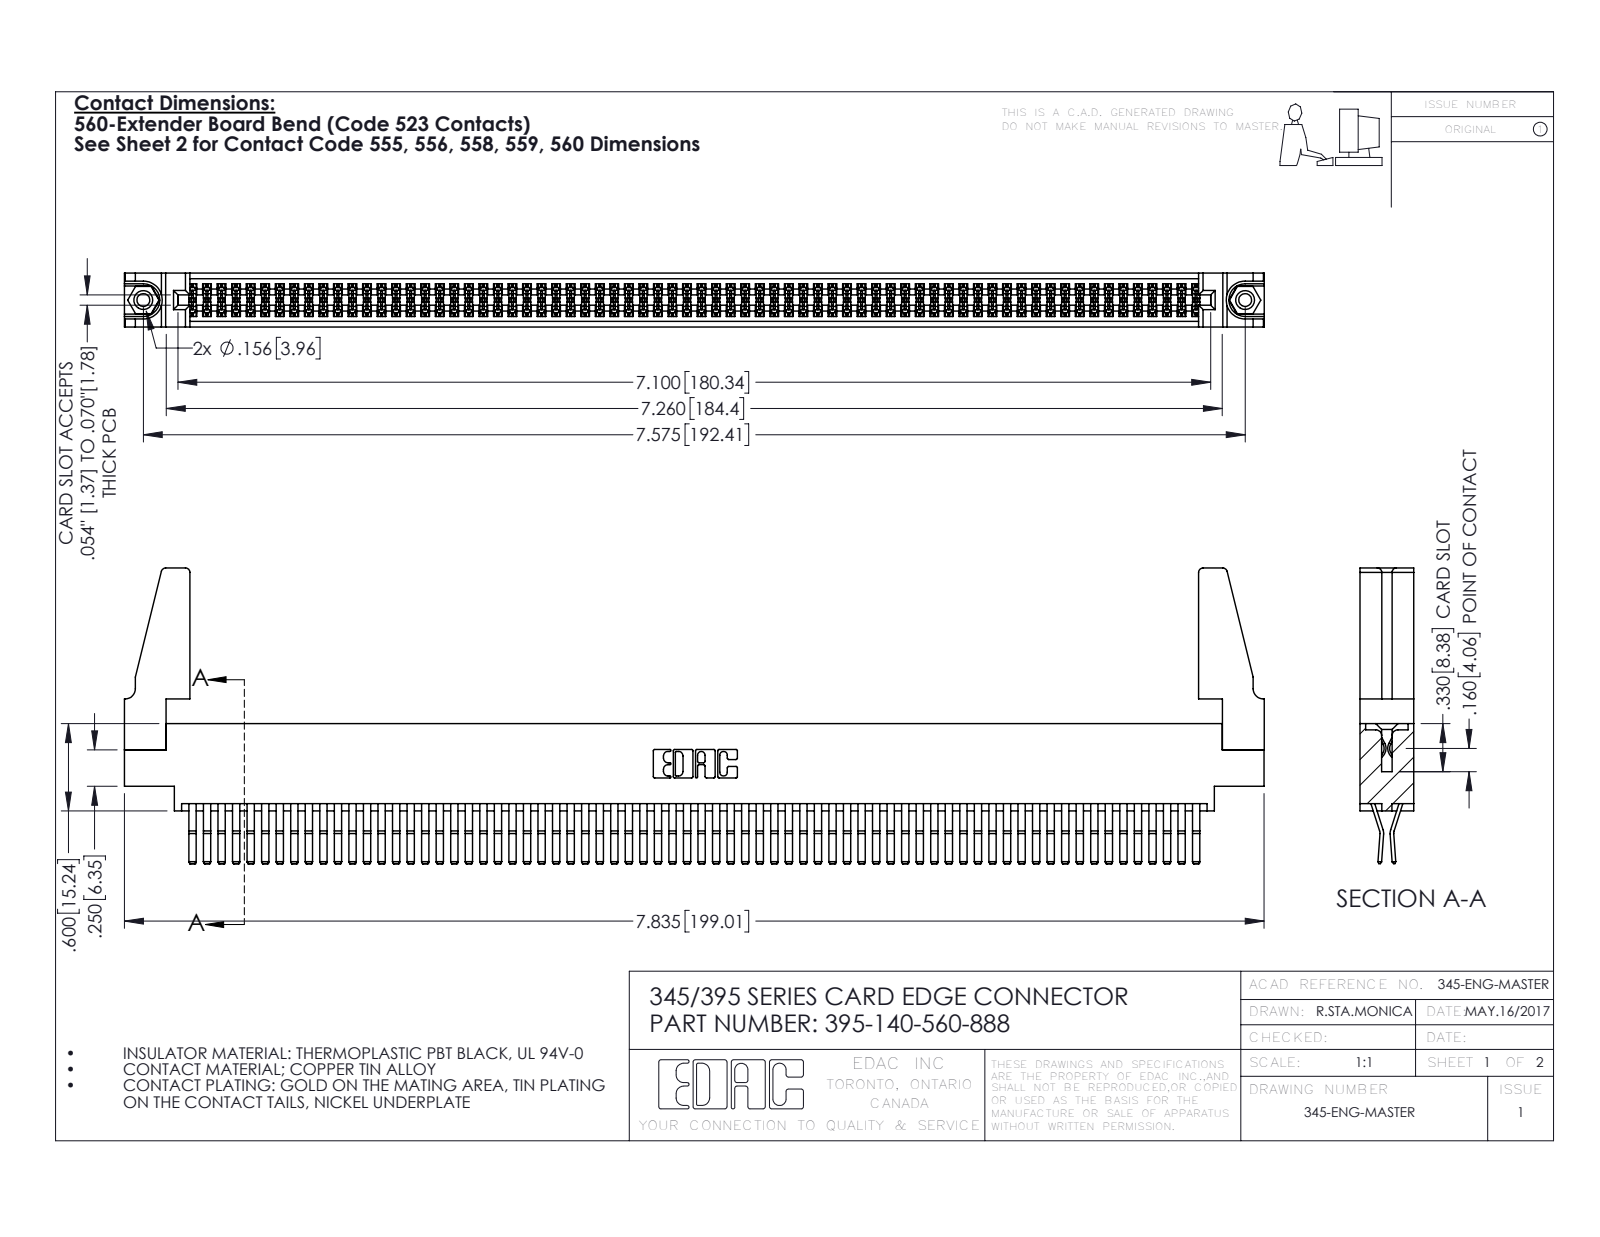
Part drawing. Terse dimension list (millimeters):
name: 345-250-001_345-250-001-102; 345-220-078_345-220-088; 395-140-560-888; 345-292-001_560 Tail (+1 more)
written by: SolidWorks 2016 (CONFIG_CONTROL_DESIGN)
unit: mm
bodies: 145 solids, 7534 faces (4776 planar, 2742 cylindrical, 16 other)
size: 199 × 51.6 × 9.4
volume: 23 650 mm³; area: 36 320 mm²
holes: 2× ⌀2.3, 2× ⌀3.2, 2× ⌀4, 1× ⌀1.6
bosses: 2× ⌀3.9
rounds: 210× R0.2, 22× R0.3, 8× R0.8, 6× R0.2, 6× R0.8, 3× R0.7, 2× R0.3, 2× R0.4
face distances: 1.8, 0.6, 7.6, 9.4, 5.1, 2.5, 6.9, 5.7, 4.4, 3.8
hole spacings: 6.9, 186.4, 192.4
